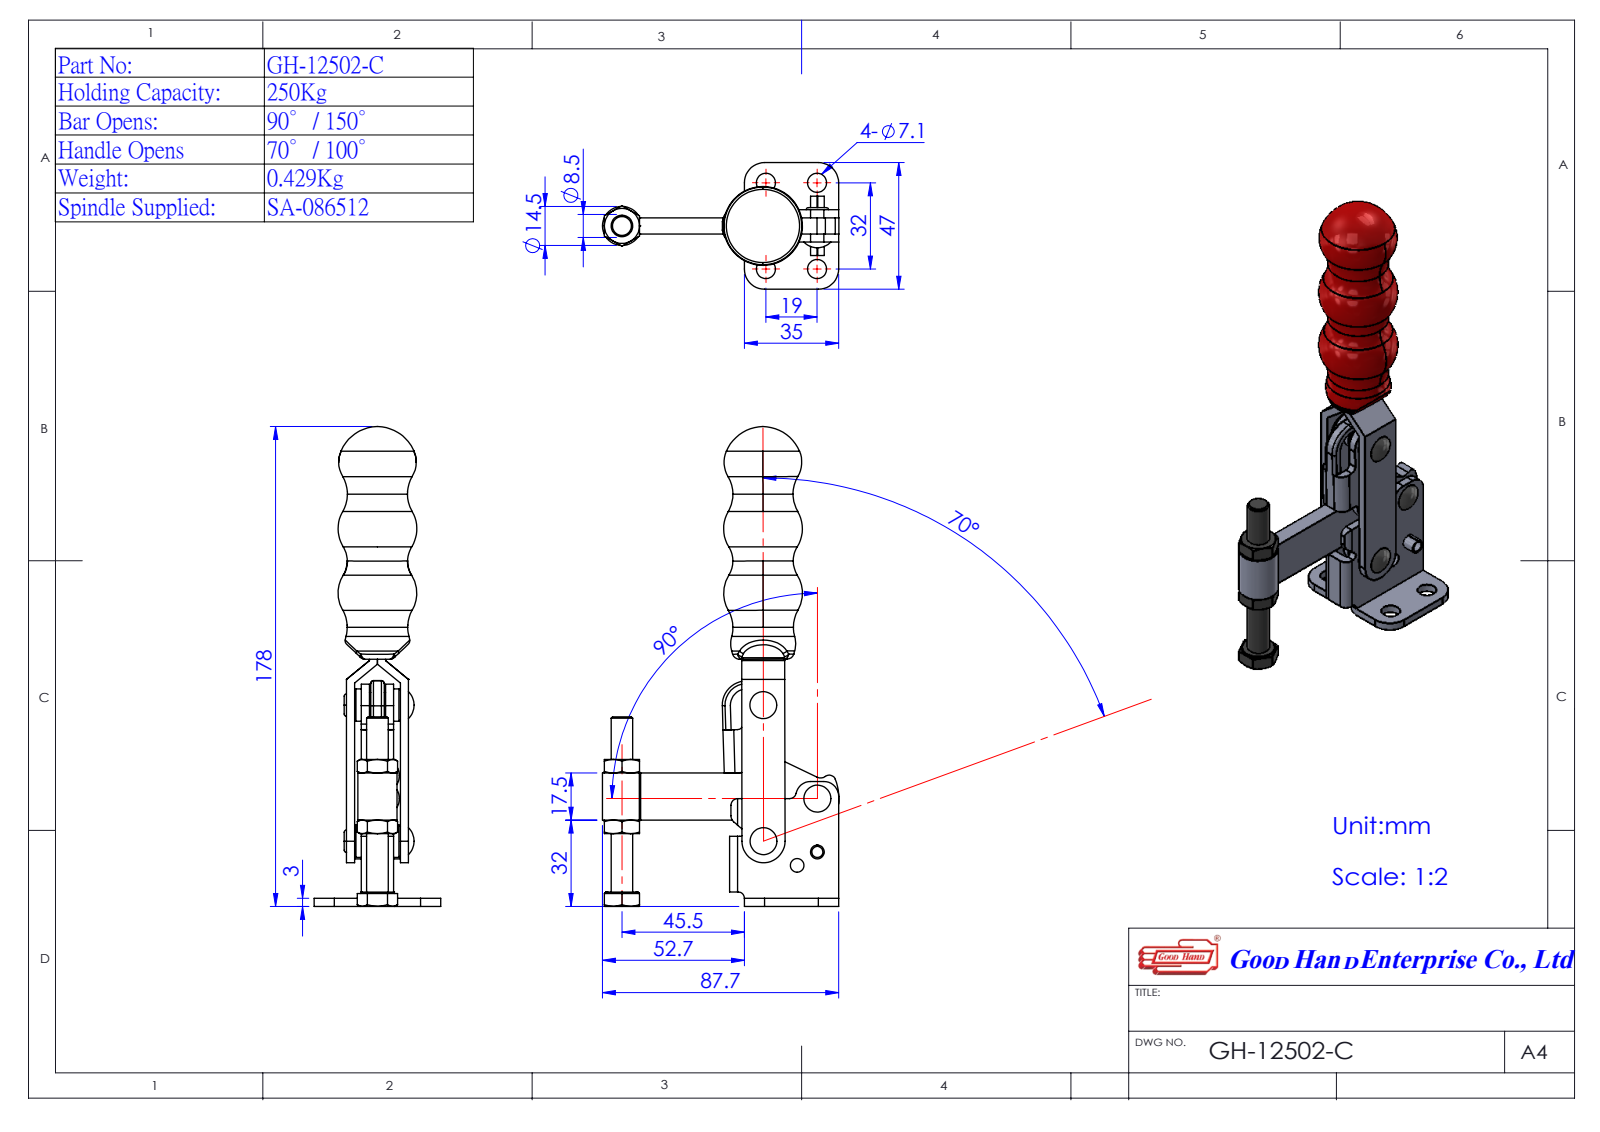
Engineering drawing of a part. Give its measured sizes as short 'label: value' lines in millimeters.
name: Group1^GH-12502-C(簡化)-1; Group2^GH-12502-C(簡化)-1; GH-SA-086512-1^GH-12502-C(簡化)-1; Group4^GH-12502-C(簡化)-1 (+2 more)
written by: SolidWorks 2016 (AUTOMOTIVE_DESIGN)
unit: mm
bodies: 5 solids, 324 faces (109 planar, 125 cylindrical, 90 other)
size: 172.7 × 87.8 × 47
volume: 72 688 mm³; area: 35 506 mm²
holes: 5× ⌀5, 4× ⌀7.1, 1× ⌀6.8, 1× ⌀8, 1× ⌀8.5
bosses: 2× ⌀10, 1× ⌀14.5, 1× ⌀12.5, 1× ⌀5
rounds: 7× R3, 4× R0.5, 4× R7.5, 3× R1, 2× R2, 2× R2.5, 2× R3.5, 2× R5.5
face distances: 3, 9, 14.5, 5.5, 6, 17.5, 12, 8.5, 11.5, 20
hole spacings: 19, 32, 37.22, 55.79, 74.2, 15.4, 21.15, 24.34
